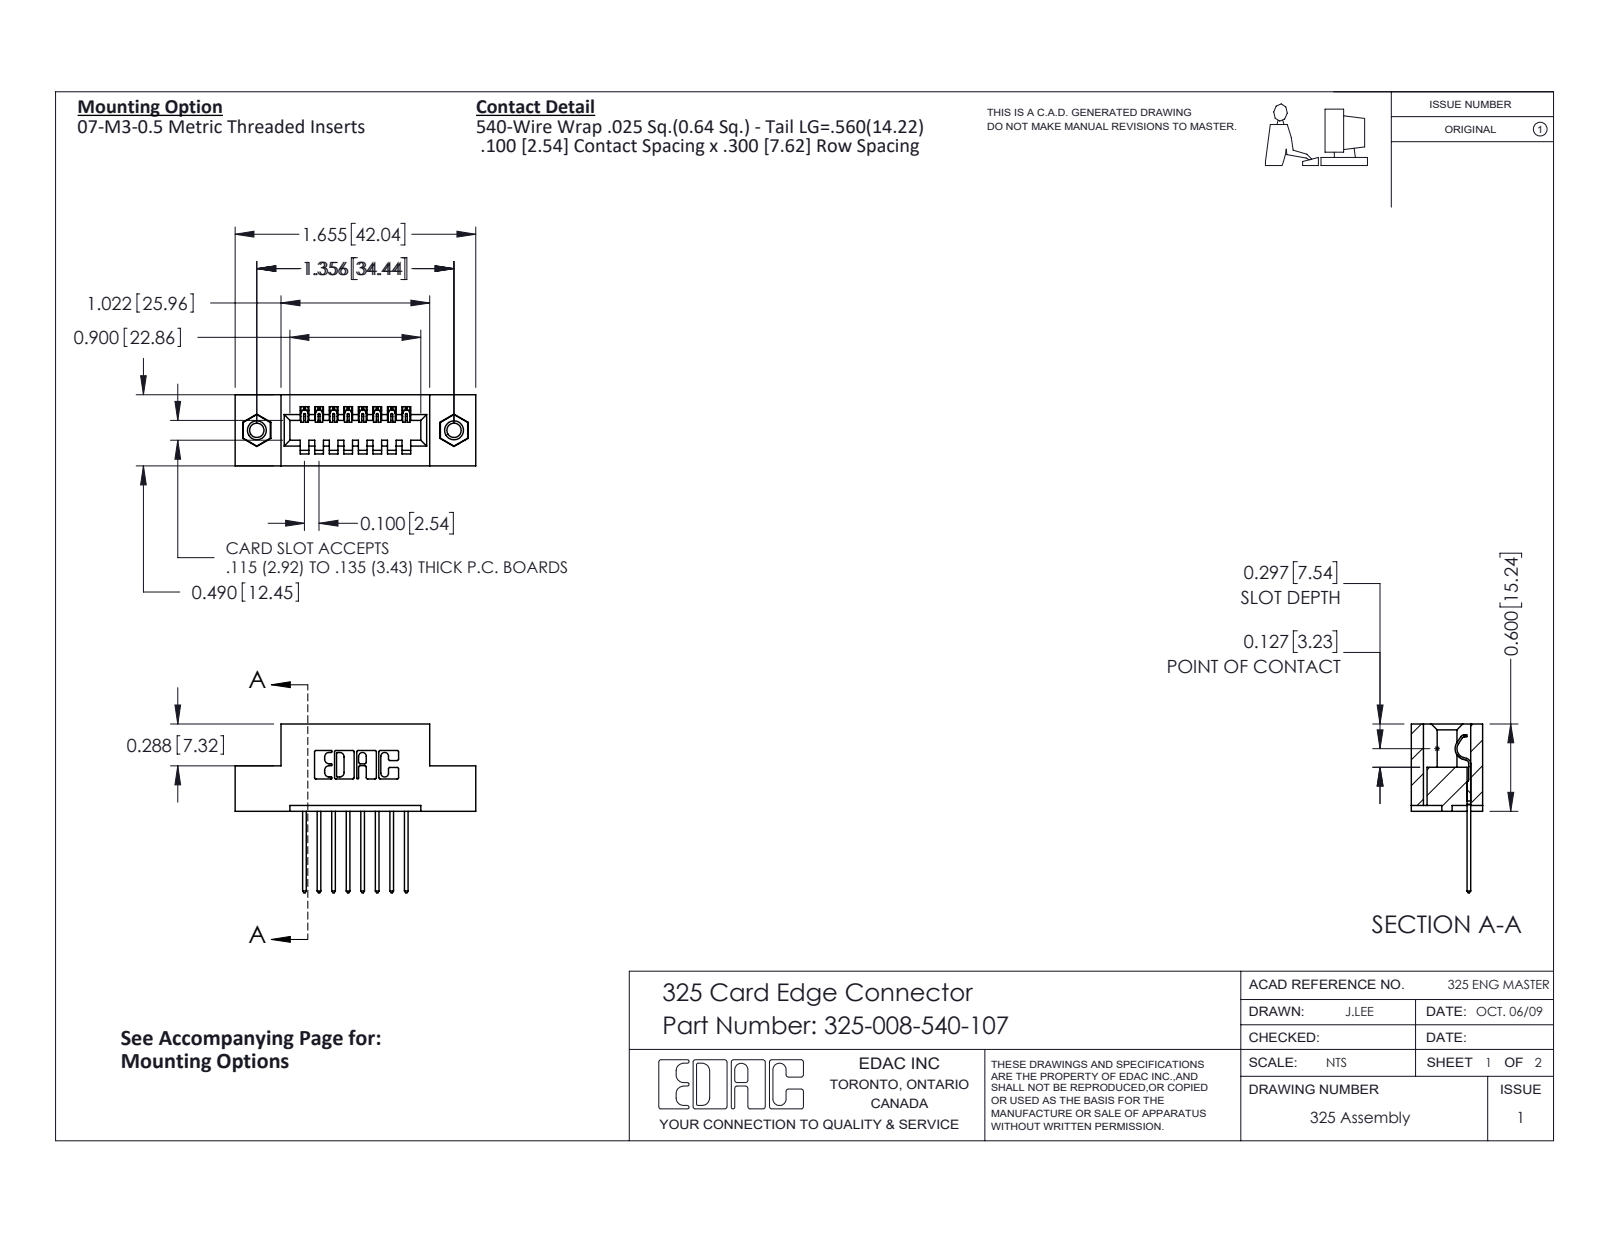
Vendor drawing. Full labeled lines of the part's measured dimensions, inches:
Part name (STEP PRODUCT): 325-292-001_325-293-140; 345-250-001_345-250-005-103; 325 Part_TI; 325-008-540-107
STEP written by: SolidWorks 2016 (CONFIG_CONTROL_DESIGN)
Units: inches
Bodies: 11 solids, 638 faces (438 planar, 184 cylindrical, 16 other)
Overall size (bounding box): 1.655 × 1.16 × 0.49
Volume: 0.309 in³ · Surface area: 7.852 in²
Round holes (diameter × count): ⌀0.098 ×2, ⌀0.125 ×2, ⌀0.16 ×2
Round bosses / shafts (diameter × count): ⌀0.155 ×2
Partial cylindrical surfaces — rounded edges, fillets, slot ends (radius × count): R0.01 ×22, R0.006 ×16, R0.01 ×16, R0.007 ×6, R0.031 ×6, R0.026 ×3, R0.014 ×1, R0.022 ×1
Main face-to-face distances: 0.3, 0.1, 0.2, 0.04, 0.083, 0.407, 0.49, 0.4, 0.06, 0.6
Hole centre spacings: 1.356
